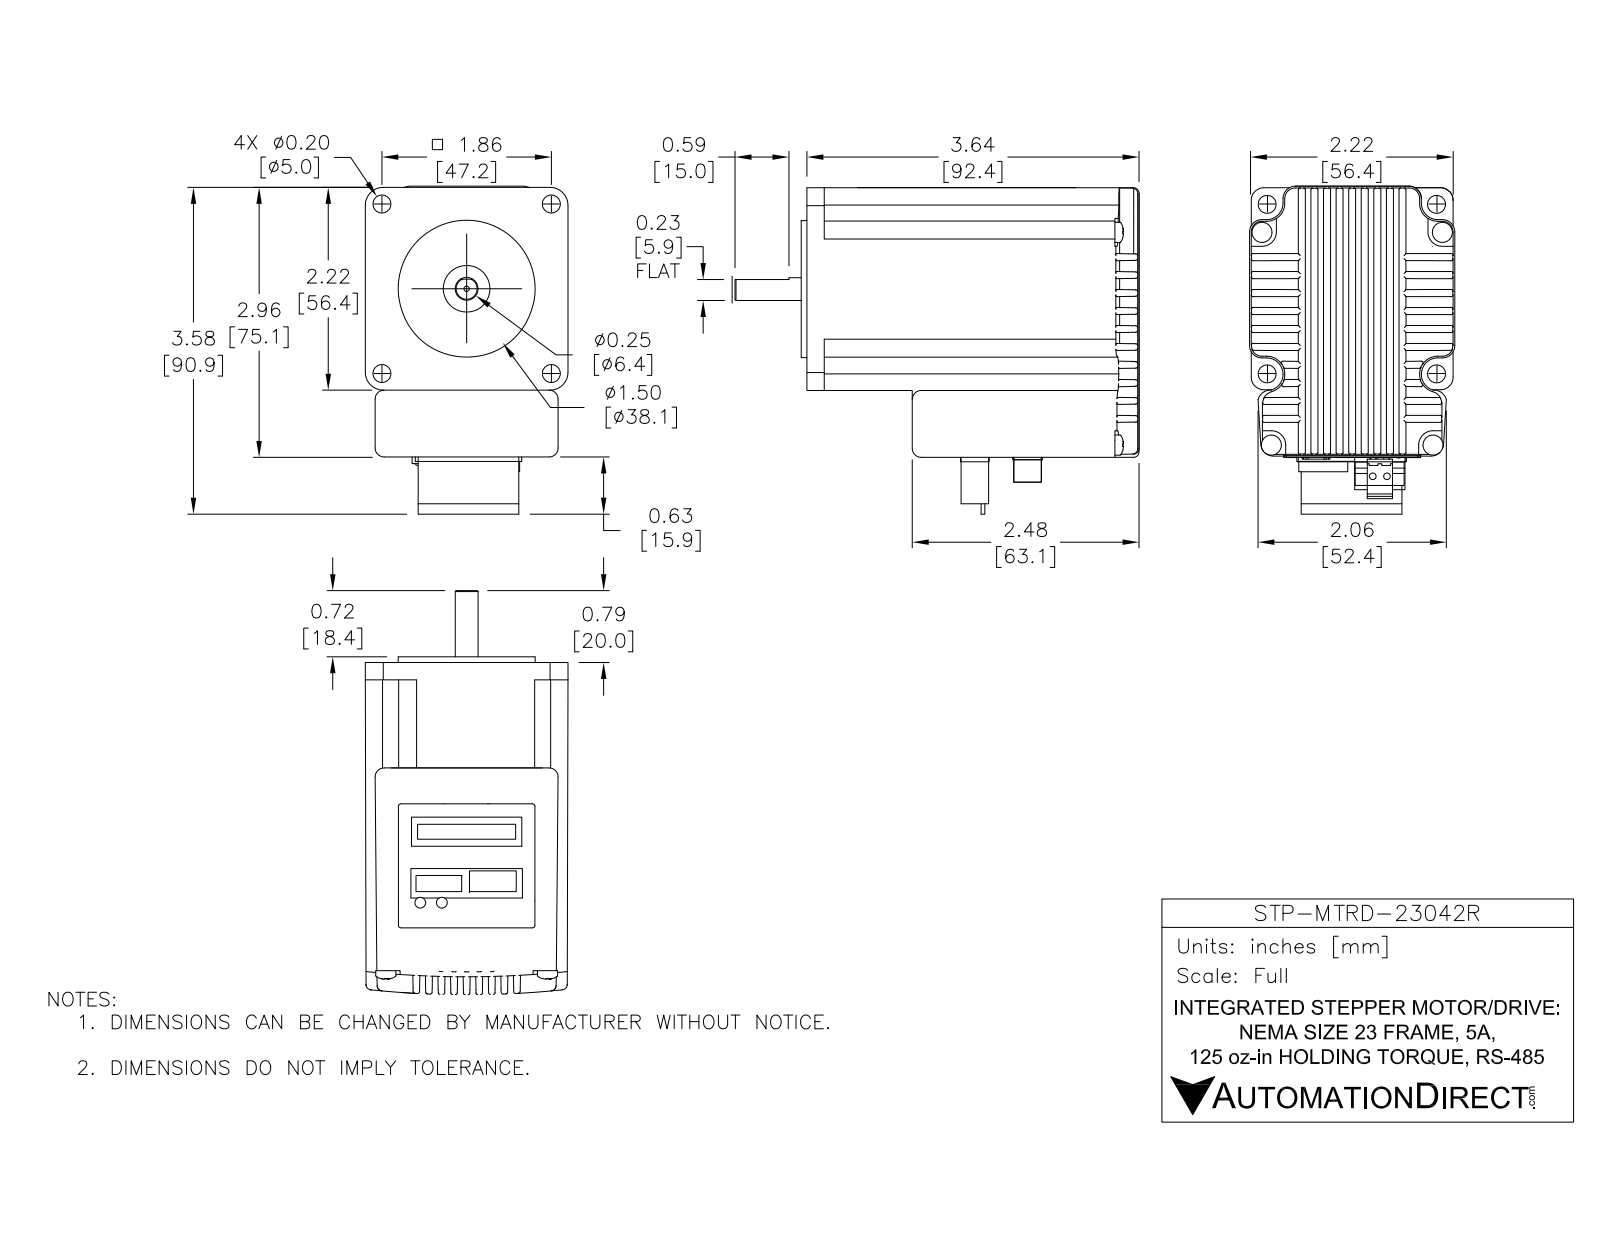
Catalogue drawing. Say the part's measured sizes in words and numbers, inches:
The part is named "STP-MTRD-23042R". Its 3-D file was written by "SolidWorks 2017 (AUTOMOTIVE_DESIGN)". It is 1 solid with 134 faces: 56 planar, 55 cylindrical and 23 other. Overall it measures 4.425 by 3.051 by 2.22 inches. Its volume is 19.71 cubic inches and its surface area 50.45 square inches. Round holes: 4 of diameter 0.197, 1 of diameter 0.059, 1 of diameter 0.511. Round bosses or shafts: 2 of diameter 0.144, 1 of diameter 1.5, 1 of diameter 0.25. Partial cylindrical surfaces (rounded edges, fillets, slot ends): 12 of radius 0.197, 9 of radius 0.059, 8 of radius 0.098, 4 of radius 0.183. The main face-to-face distances are 2.22, 2.953, 3.638, 0.108, 2.112, 0.732, 3.701, 0.063, 2.004, 2.504. The hole center spacings are 1.312, 1.856, 2.625.
